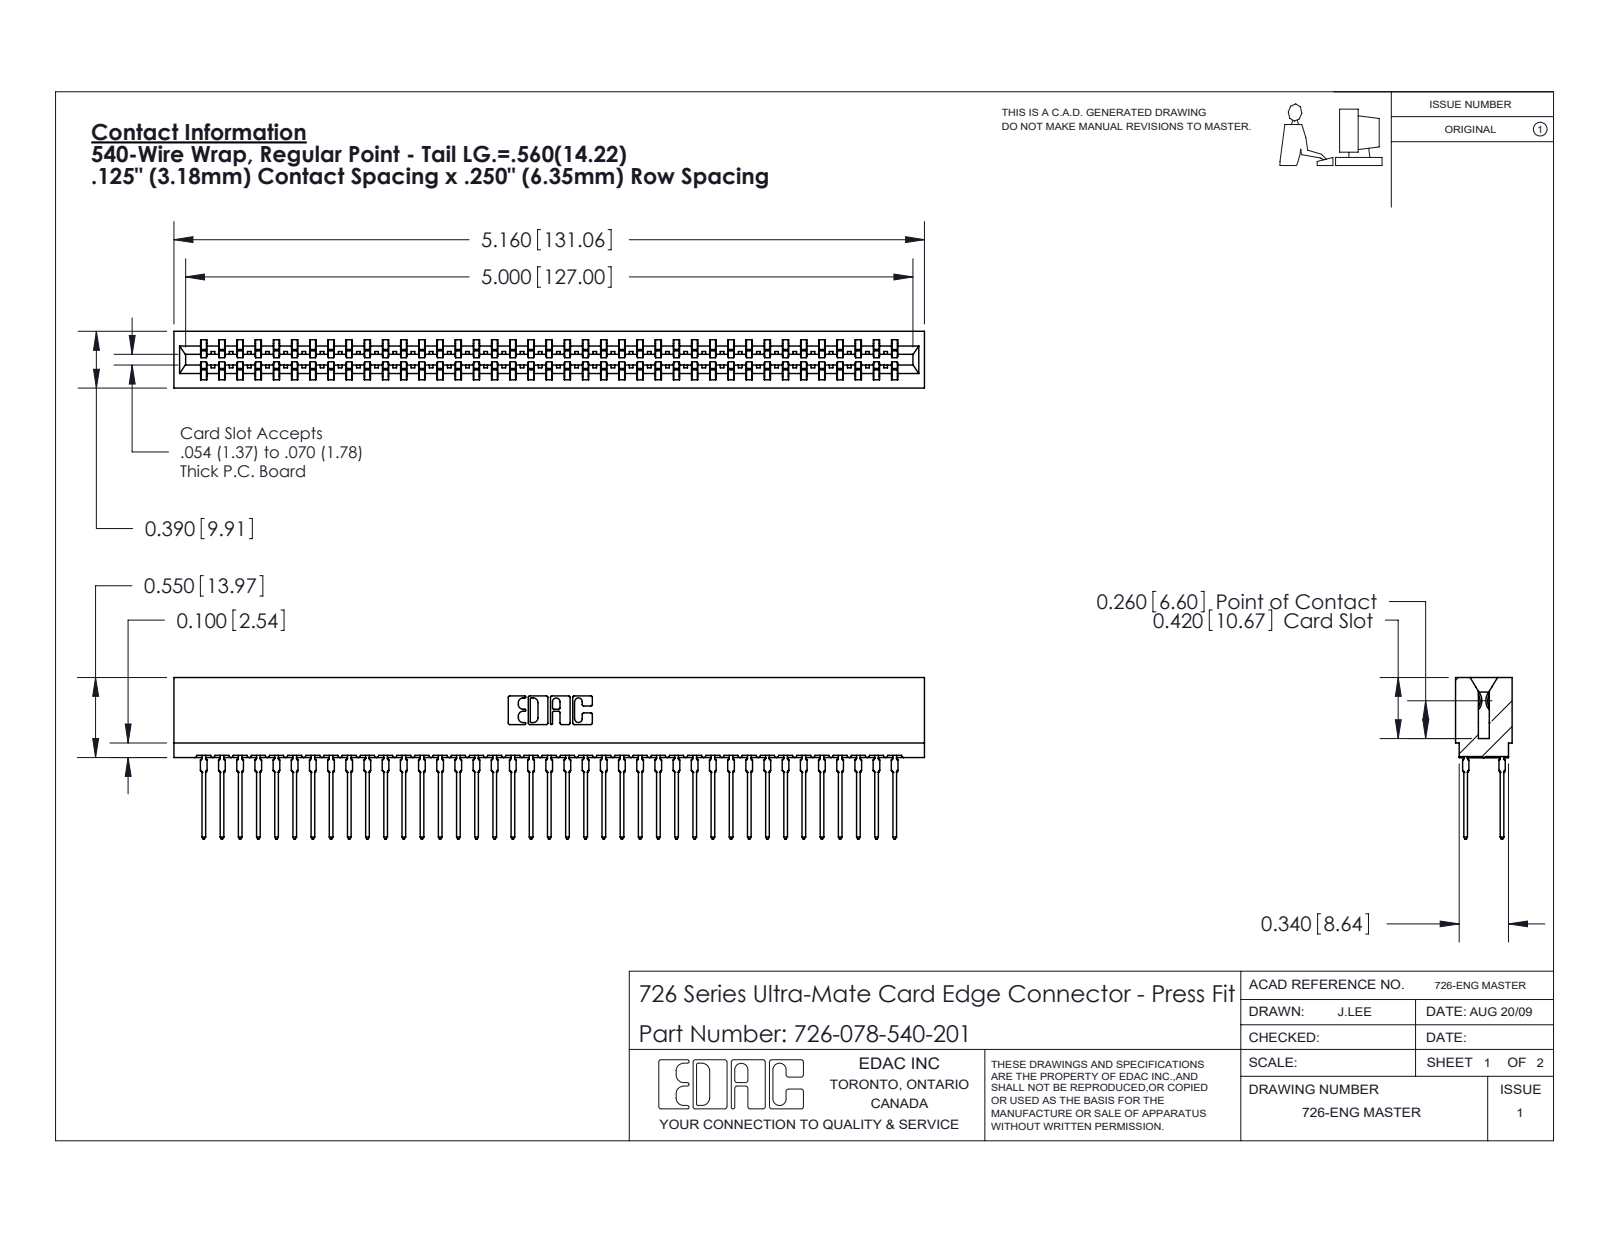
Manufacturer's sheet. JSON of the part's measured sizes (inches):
{"part_name": "726 Part_.515 Slot Depth - 01; 726-078-540-201; 746-292-001_540", "step_written_by": "SolidWorks 2020 (CONFIG_CONTROL_DESIGN)", "units": "inches", "bodies": {"solids": 79, "faces": 7078, "planar": 3643, "cylindrical": 1407, "other": 2028}, "overall_size": [5.16, 1.109, 0.39], "volume_in3": 0.752, "surface_area_in2": 33.42, "partial_cylinders_radius": [[0.021, 156], [0.015, 40], [0.01, 22], [0.005, 8], [0.011, 8], [0.007, 6], [0.031, 6], [0.026, 3]], "face_to_face_distances": [0.057, 0.333, 0.025, 0.307, 0.39, 0.25, 0.083, 0.275, 0.365, 0.032]}
